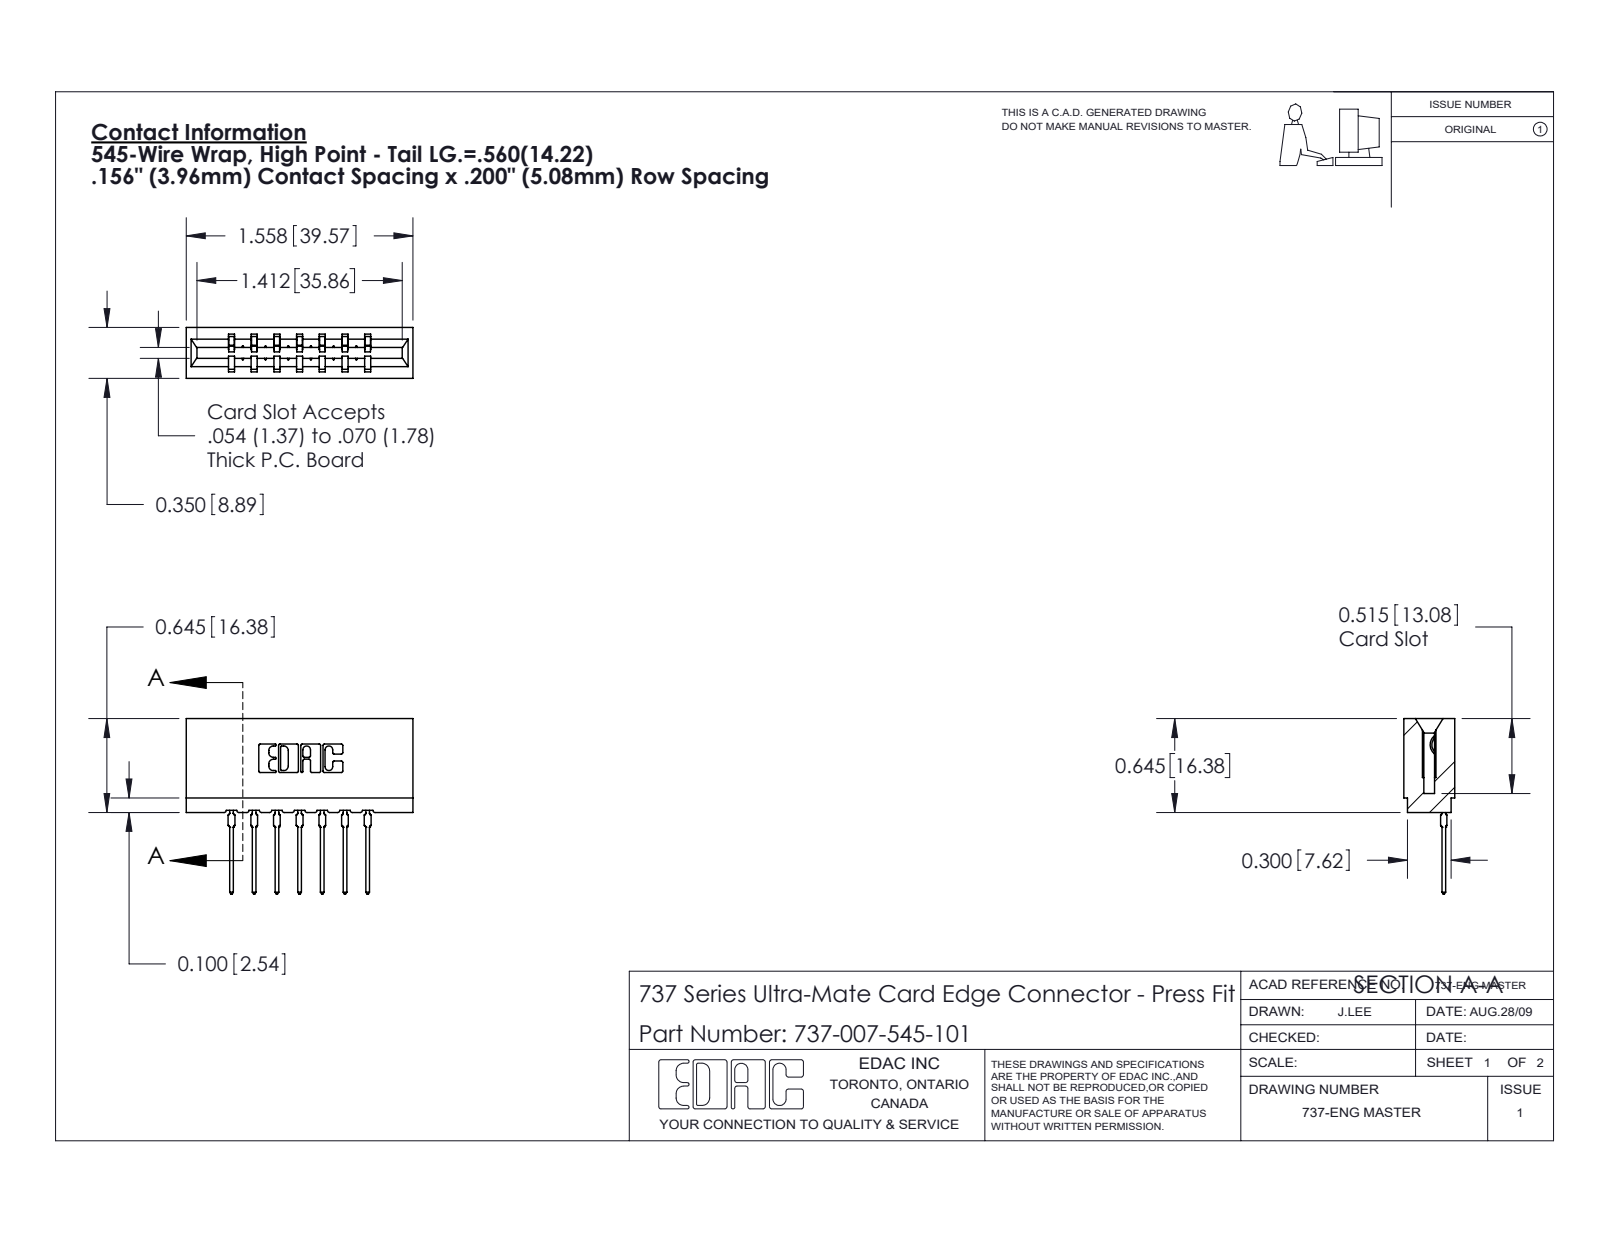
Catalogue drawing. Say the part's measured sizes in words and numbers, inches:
The part is named "745-292-001_545; 737 Part_Insulator Option - 01; 737-007-545-101". Its 3-D file was written by "SolidWorks 2020 (CONFIG_CONTROL_DESIGN)". It is 8 solids with 885 faces: 530 planar, 173 cylindrical and 182 other. Overall it measures 1.558 by 1.206 by 0.35 inches. Its volume is 0.25 cubic inches and its surface area 7.686 square inches. Partial cylindrical surfaces (rounded edges, fillets, slot ends): 22 of radius 0.01, 14 of radius 0.015, 14 of radius 0.021, 6 of radius 0.007, 6 of radius 0.031, 4 of radius 0.005, 4 of radius 0.011, 3 of radius 0.026. The main face-to-face distances are 0.156, 0.138, 0.212, 0.35, 0.312, 0.354, 0.198, 0.624, 0.468, 0.074.
